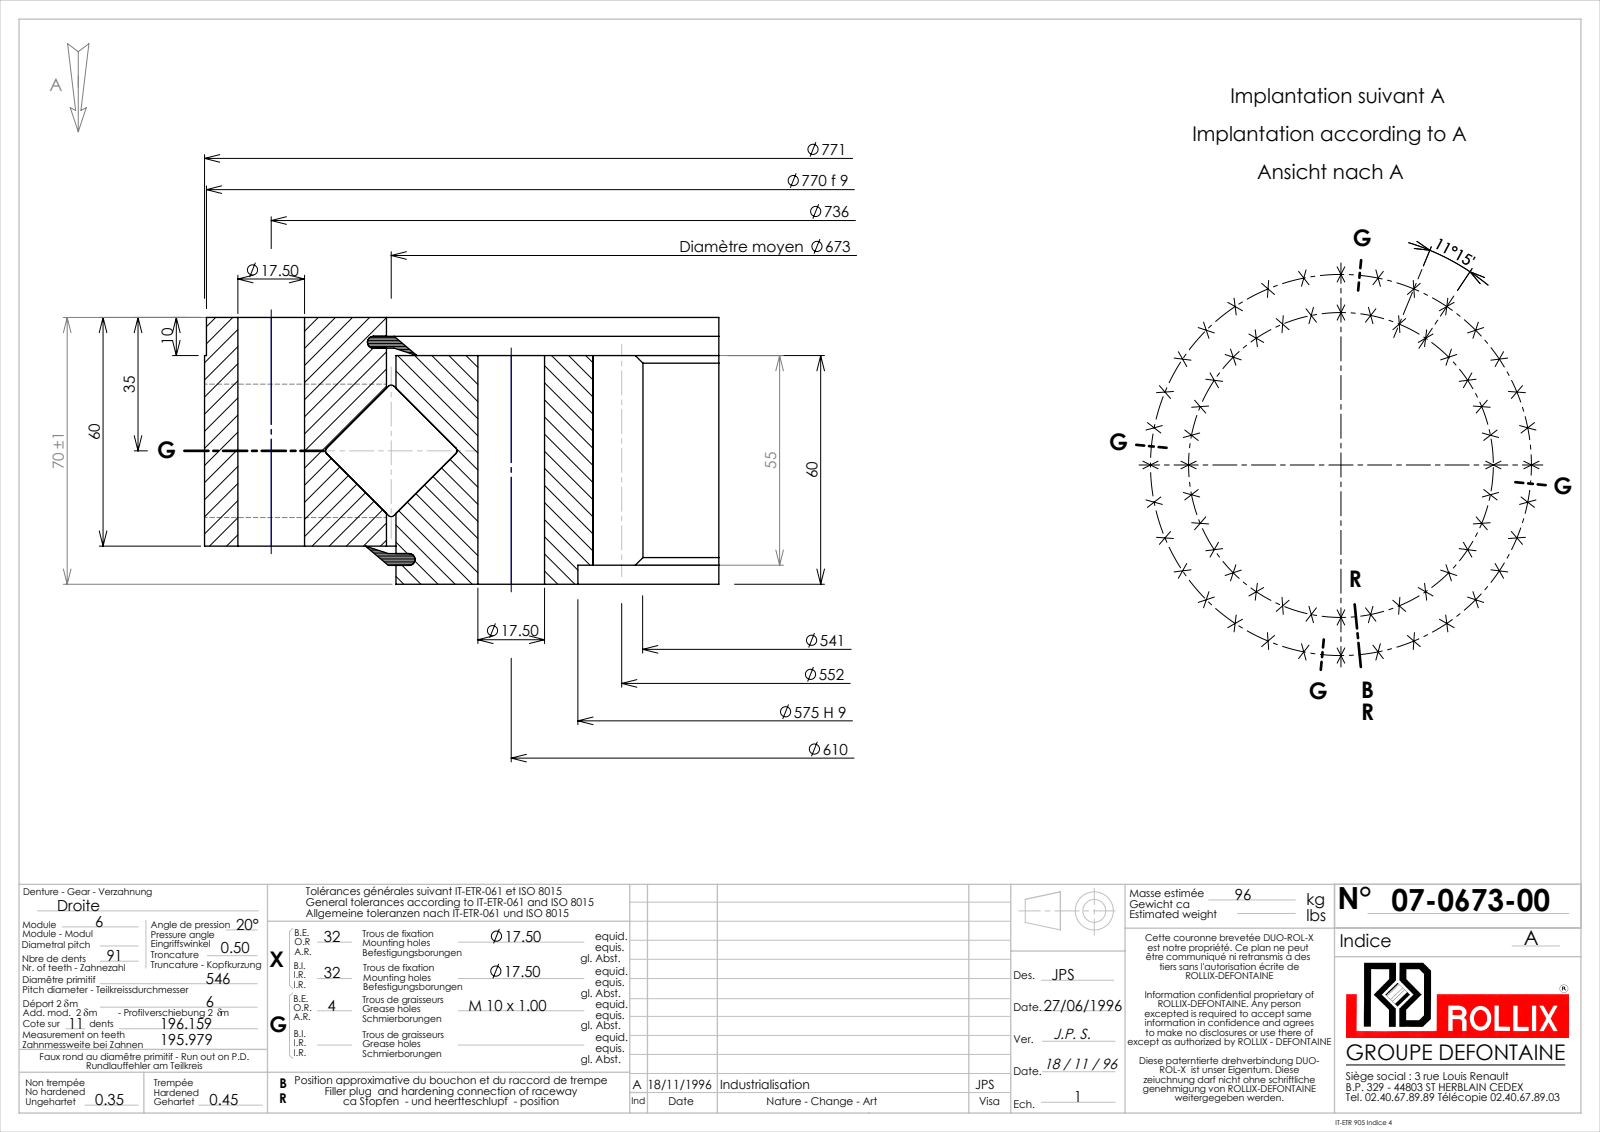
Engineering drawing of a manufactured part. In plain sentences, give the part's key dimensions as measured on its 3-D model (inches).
The part is named "07-0673-00". Its 3-D file was written by "SolidWorks 2016 (CONFIG_CONTROL_DESIGN)". It is 5 solids with 769 faces: 198 planar, 339 cylindrical and 232 other. Overall it measures 30.354 by 30.354 by 2.756 inches. Its volume is 681.6 cubic inches and its surface area 2 232 square inches. Round holes: 64 of diameter 0.689, 4 of diameter 0.354, 1 of diameter 22.638, 1 of diameter 26.594. Round bosses or shafts: 1 of diameter 30.354, 1 of diameter 30.315, 1 of diameter 26.398, 1 of diameter 0.984. Partial cylindrical surfaces (rounded edges, fillets, slot ends): 1 of radius 10.65, 1 of radius 11.161. The main face-to-face distances are 0.394, 2.362, 1.969, 2.756, 0.195, 2.561, 0.199, 2.167, 0.317, 2.439. The hole center spacings are 12.008, 11.321, 23.554, 9.191, 19.969, 2.354, 13.343, 15.235.
